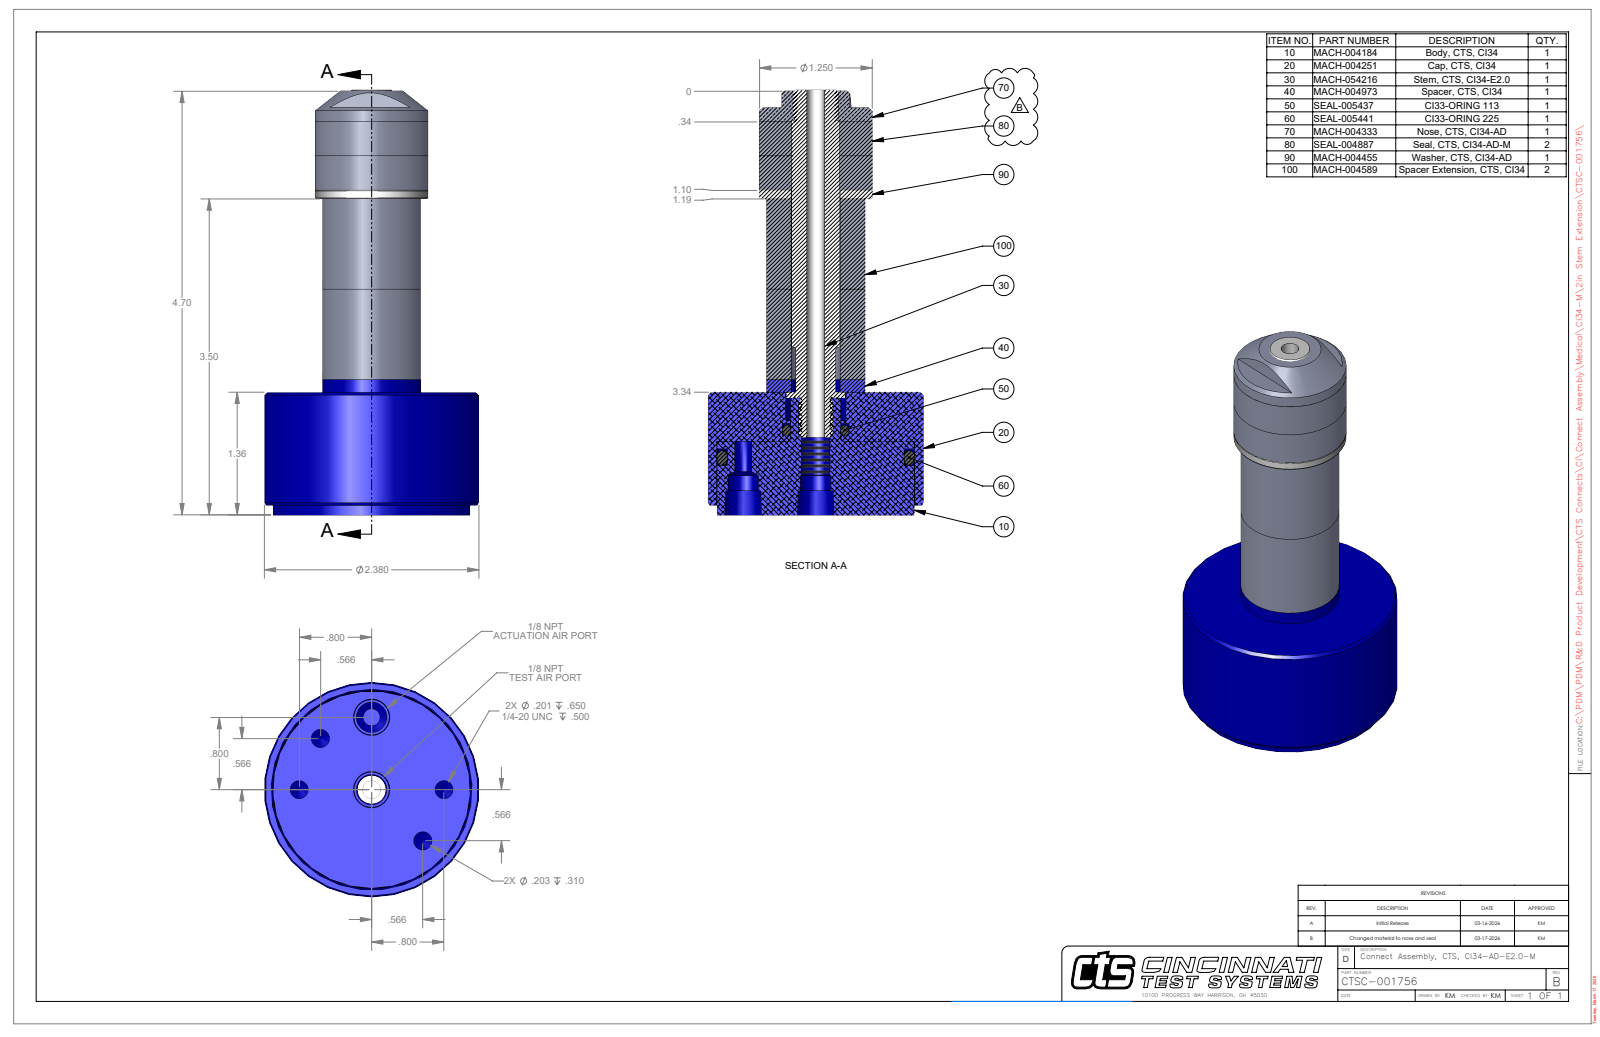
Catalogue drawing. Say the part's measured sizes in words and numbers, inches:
The part is named "CTSC-001756". Its 3-D file was written by "SolidWorks 2023 (AUTOMOTIVE_DESIGN)". It is 8 solids with 78 faces: 37 planar, 28 cylindrical and 13 other. Overall it measures 4.706 by 2.38 by 2.38 inches. Its volume is 9.047 cubic inches and its surface area 58.45 square inches. Round holes: 2 of diameter 0.201, 2 of diameter 0.203, 1 of diameter 0.203, 1 of diameter 0.313, 1 of diameter 0.339, 1 of diameter 0.422, 1 of diameter 0.53, 1 of diameter 0.541, 1 of diameter 0.546, 1 of diameter 0.661, 1 of diameter 2.188. Round bosses or shafts: 1 of diameter 2.38, 1 of diameter 2.178, 1 of diameter 1.25, 1 of diameter 1.09, 1 of diameter 0.65, 1 of diameter 0.529, 1 of diameter 0.5. The main face-to-face distances are 1.36, 1, 4.357, 2.997, 3.977, 2.617, 0.38, 3.597, 2.237, 0.38. The hole center spacings are 0.8, 0.612, 1.478, 1.6.
